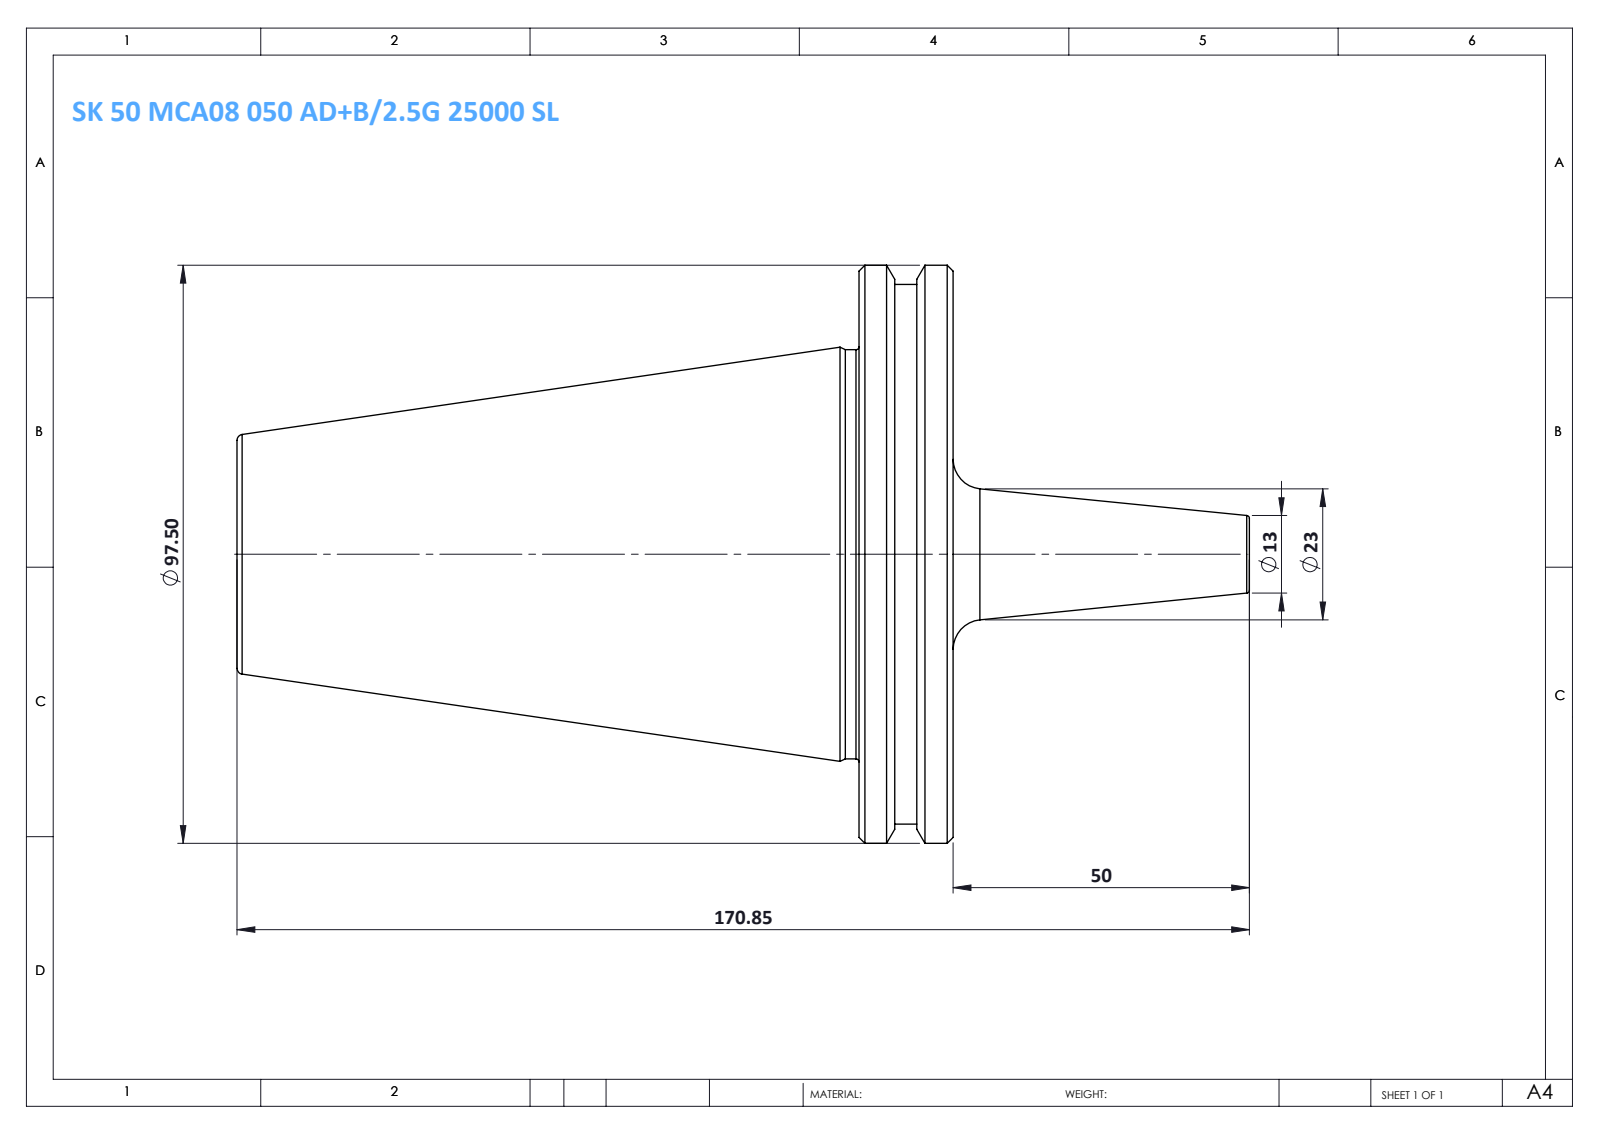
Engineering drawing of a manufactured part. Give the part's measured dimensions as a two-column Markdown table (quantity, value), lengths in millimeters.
| quantity | value |
| --- | --- |
| part name | SK 50 MCA08 050 AD+B-2.5G25000 SL |
| STEP written by | SolidWorks 2014 (CONFIG_CONTROL_DESIGN) |
| units | millimeters |
| bodies | 1 solid, 36 faces (6 planar, 8 cylindrical, 22 other) |
| overall size | 170.85 × 97.5 × 97.5 |
| volume | 386 914 mm³ |
| surface area | 39 040 mm² |
| round bosses / shafts (diameter × count) | 97.5 × 1, 91 × 1, 69 × 1 |
| main face-to-face distances | 15.9, 120.85, 104.95, 6.13, 9.77, 114.72, 9.88, 3.75, 6.02, 110.97 |
